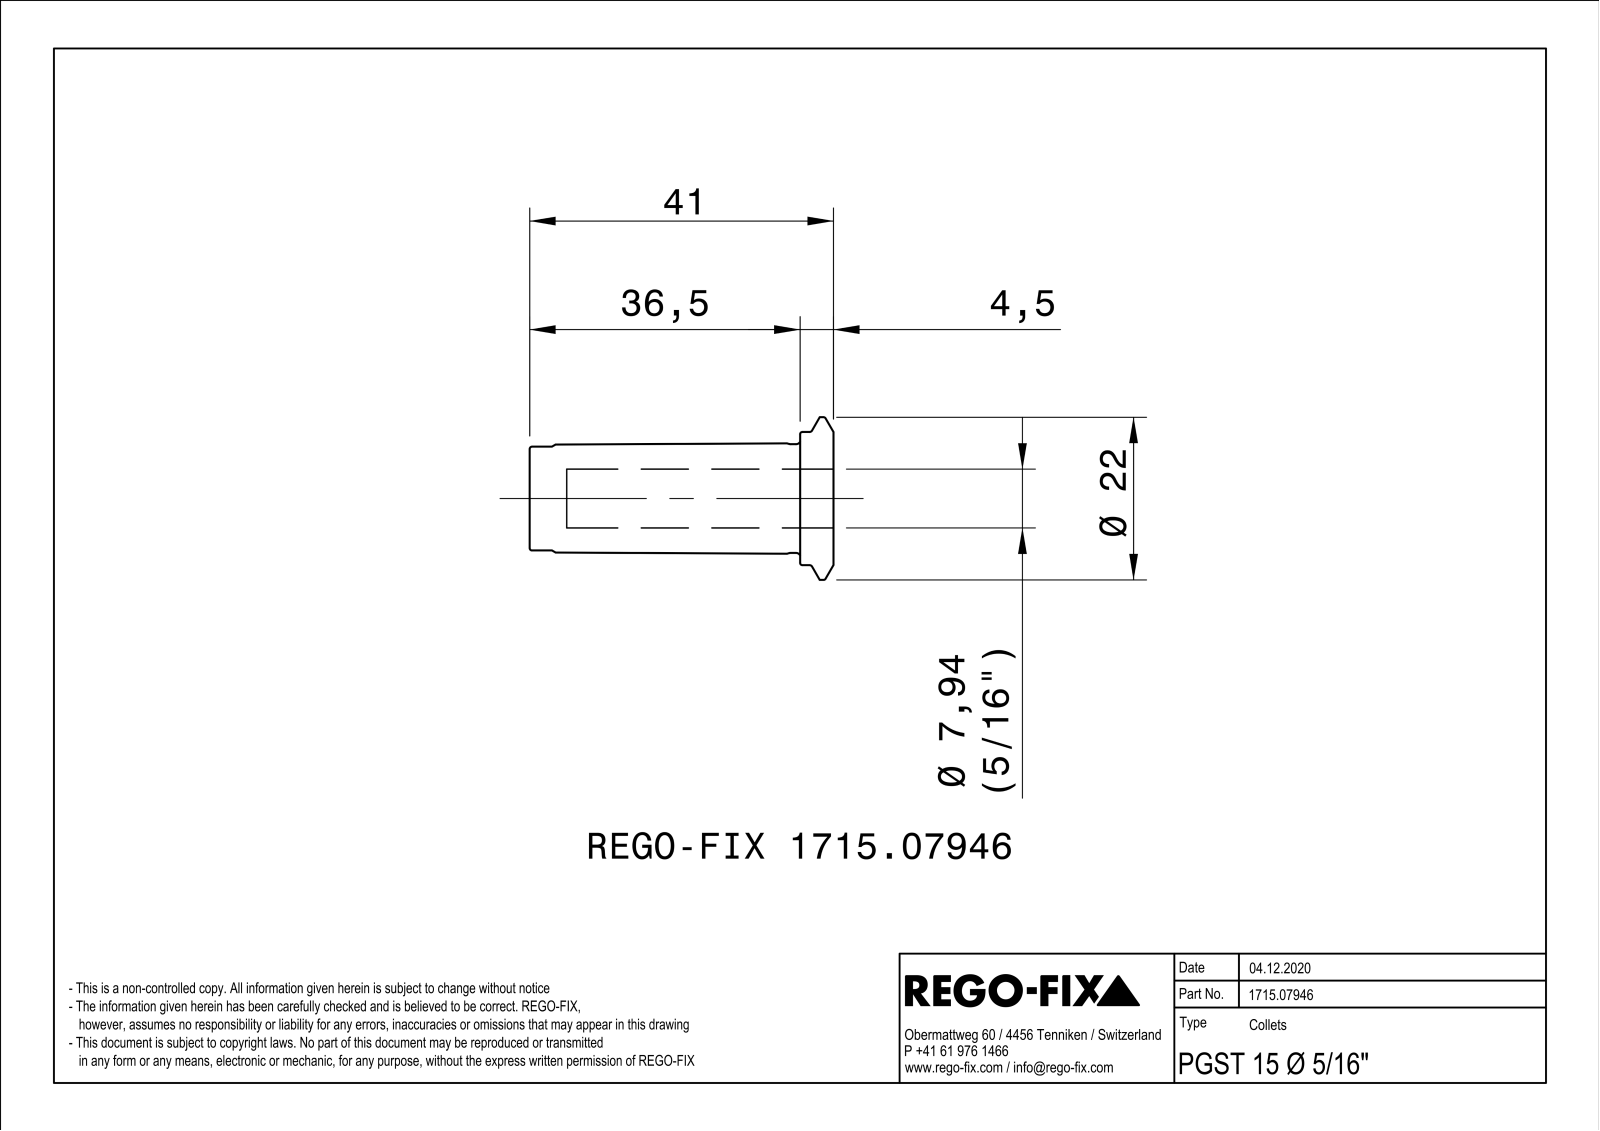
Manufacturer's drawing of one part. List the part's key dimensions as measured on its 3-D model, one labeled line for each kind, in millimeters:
Part name (STEP PRODUCT): NOCUT
STEP written by: SIEMENS PLM Software Solid Edge ST10 (AUTOMOTIVE_DESIGN)
Units: millimetres
Bodies: 2 solids, 48 faces (12 planar, 14 cylindrical, 22 other)
Overall size (bounding box): 41 × 21.98 × 21.98
Volume: 5 668 mm³ · Surface area: 4 020 mm²
Round holes (diameter × count): ⌀1.5 ×3, ⌀3 ×1, ⌀7.93 ×1, ⌀10 ×1, ⌀11.46 ×1, ⌀12.5 ×1
Round bosses / shafts (diameter × count): ⌀21.98 ×1, ⌀18 ×1, ⌀14.7 ×1, ⌀14 ×1, ⌀12 ×1, ⌀11.1 ×1
Main face-to-face distances: 4.5, 36.5, 41, 32, 36, 31.5, 0.5, 5, 2
Hole centre spacings: 4, 6.93, 6.92
